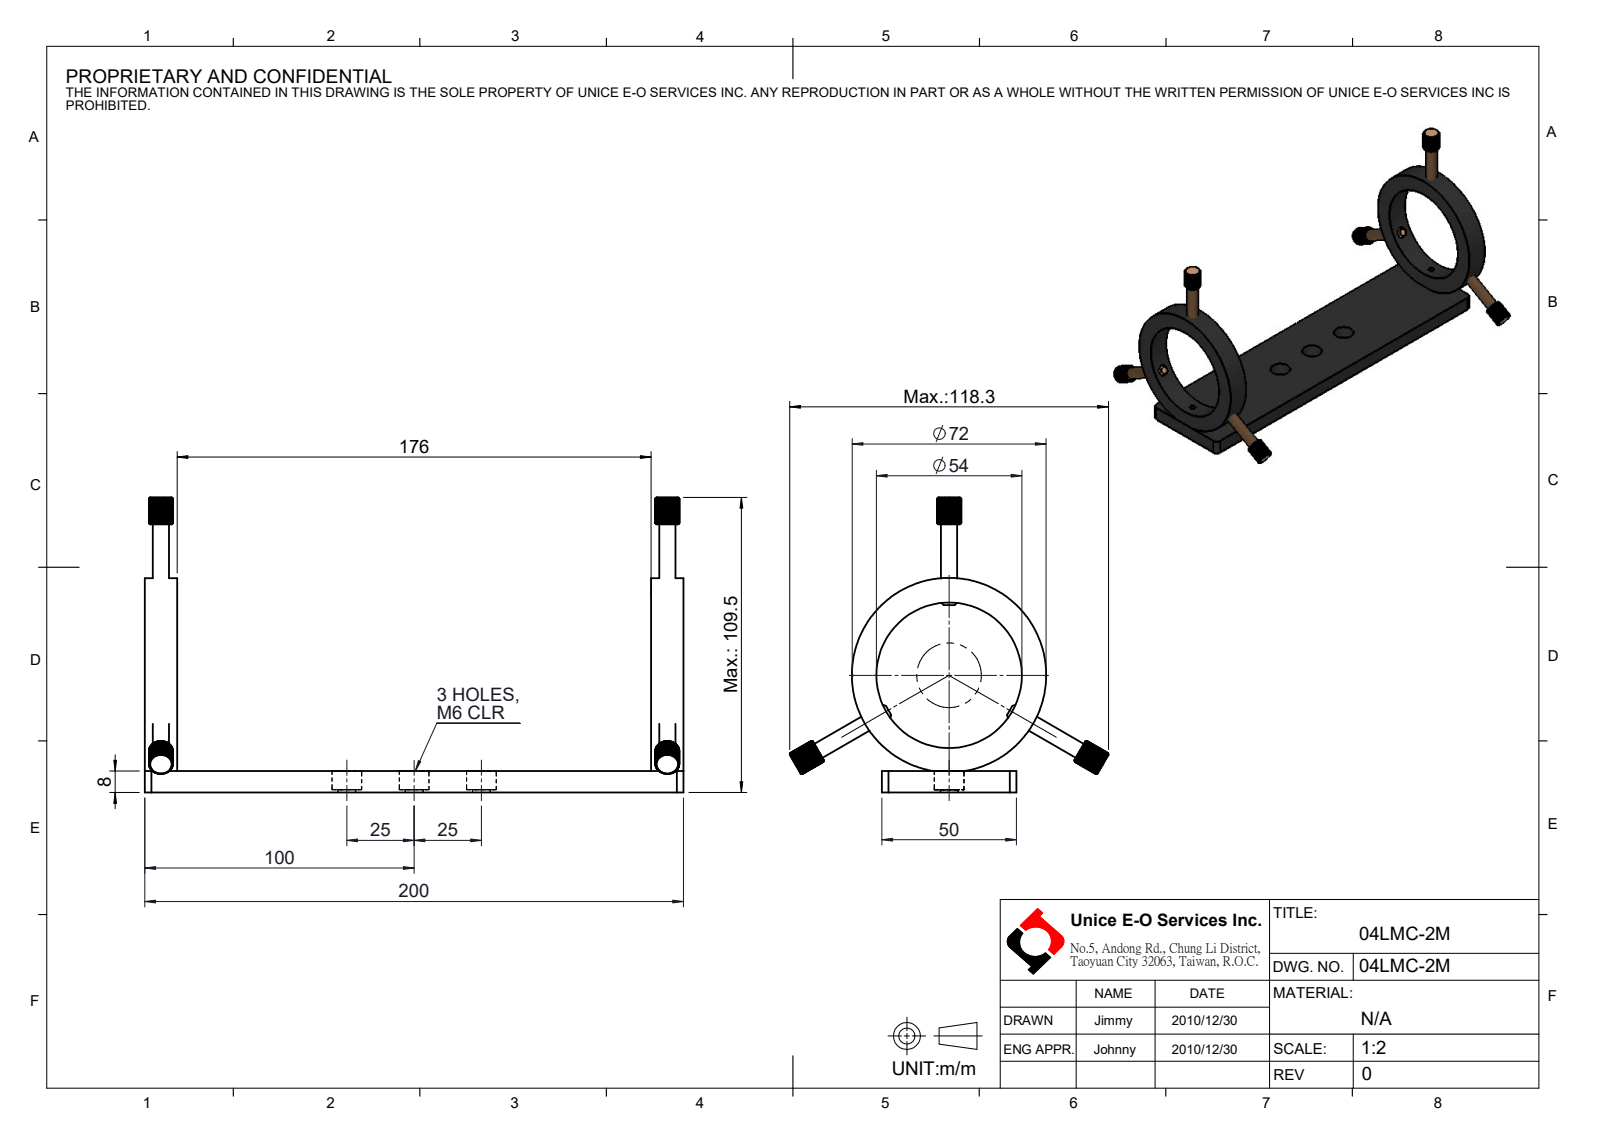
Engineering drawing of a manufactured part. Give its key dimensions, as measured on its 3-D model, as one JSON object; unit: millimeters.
{"part_name": "04LMC-2M", "step_written_by": "SolidWorks 2016 (CONFIG_CONTROL_DESIGN)", "units": "millimeters", "bodies": {"solids": 9, "faces": 943, "planar": 575, "cylindrical": 332, "other": 36}, "overall_size": [200, 118.31, 109.5], "volume_mm3": 127316, "surface_area_mm2": 49083, "round_holes": [[5, 6], [6.6, 3], [11, 3], [3.3, 2], [4.5, 2], [8, 2], [54, 1]], "round_bosses_or_shafts": [[6, 6], [72, 1]], "partial_cylinders_radius": [[4.5, 6], [2.5, 4]], "face_to_face_distances": [8, 188, 12, 200, 176, 50, 7, 1, 10, 101.5], "hole_center_spacings": [188, 25, 69, 94, 119, 50]}
